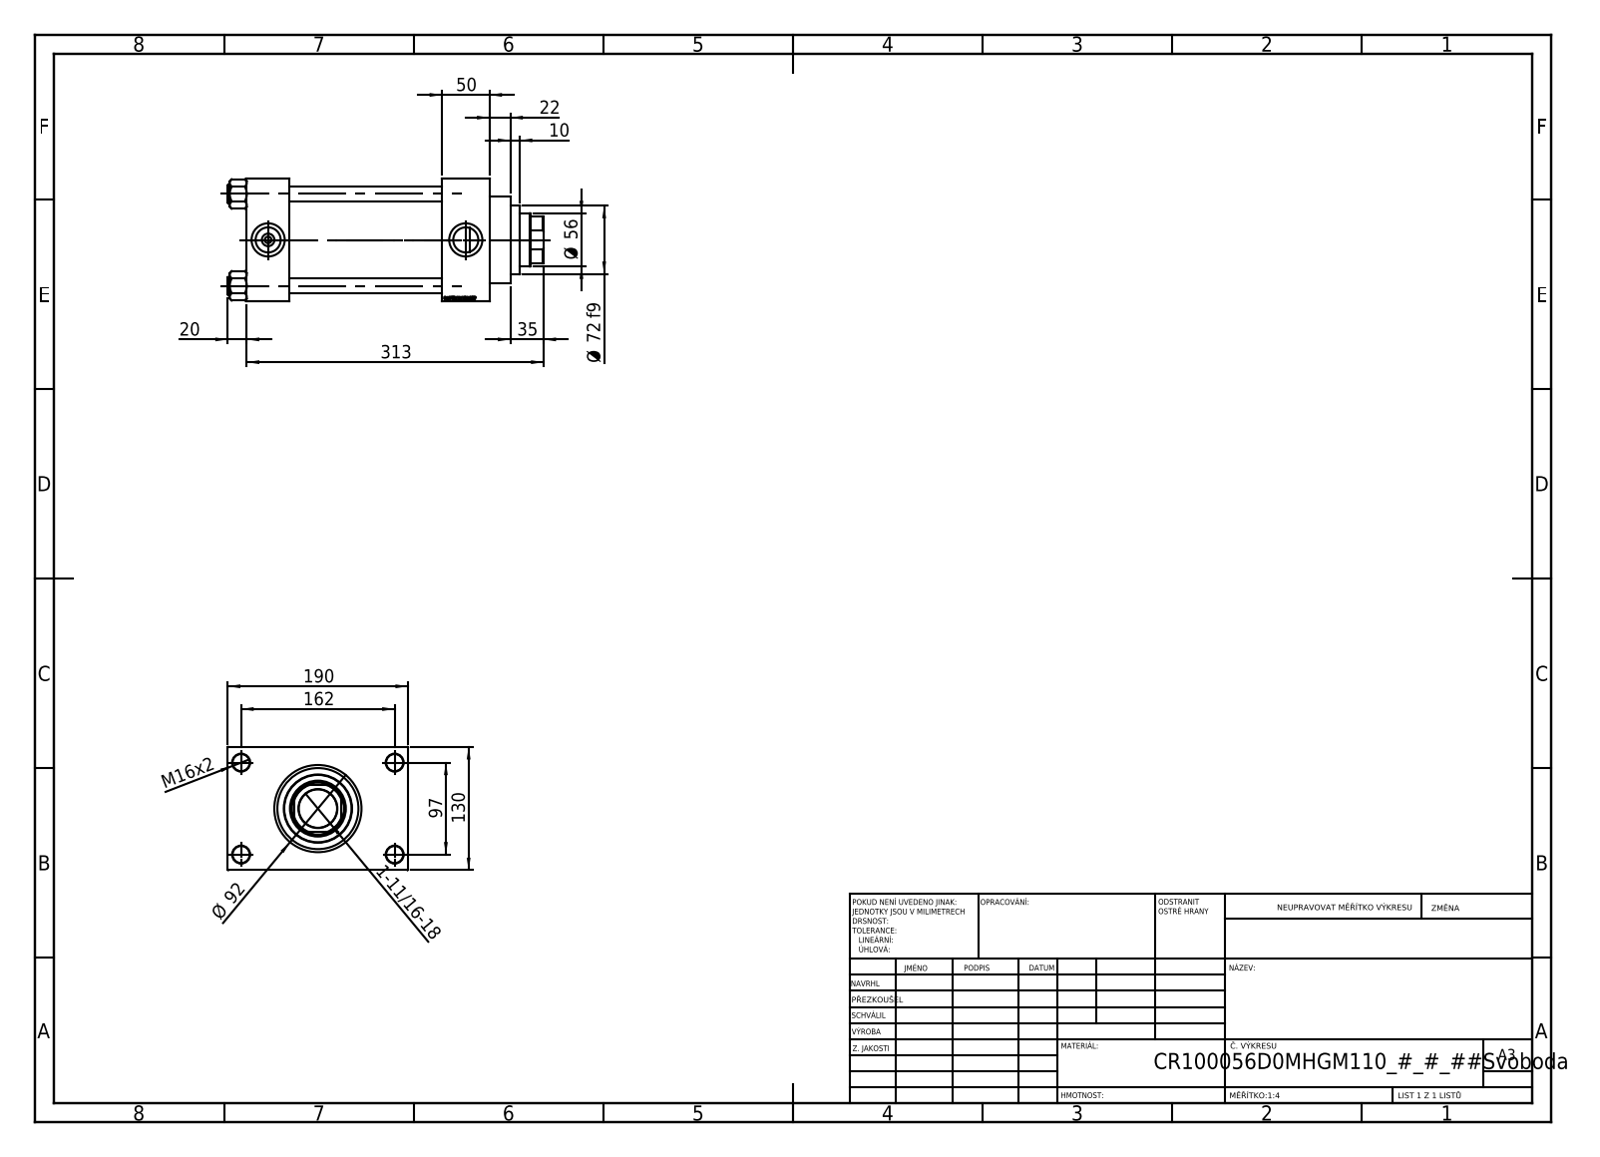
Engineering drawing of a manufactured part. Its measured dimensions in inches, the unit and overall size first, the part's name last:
Units: inches
Overall size (bounding box): 13.11 × 7.48 × 5.118
Round holes (diameter × count): ⌀0.63 ×4, ⌀0.709 ×4, ⌀0.276 ×2, ⌀1.041 ×2, ⌀1.378 ×2, ⌀1.594 ×1, ⌀2.205 ×1, ⌀2.323 ×1, ⌀2.992 ×1, ⌀3.366 ×1, ⌀3.937 ×1
Round bosses / shafts (diameter × count): ⌀0.748 ×4, ⌀4.173 ×1, ⌀3.622 ×1, ⌀2.835 ×1
Partial cylindrical surfaces — rounded edges, fillets, slot ends (radius × count): R1.063 ×1
Main face-to-face distances: 5.118, 1.969, 1.772, 8.11, 6.339, 10.079, 8.307, 6.299, 1.181, 7.48
Hole centre spacings: 1.281, 2.698, 3.717, 3.815, 4.026, 5.096, 6.367, 3.819
Volume: 183.6 in³ · Surface area: 704.5 in²
Bodies: 11 solids, 1151 faces (545 planar, 88 cylindrical, 518 other)
Part name (STEP PRODUCT): V215CR_D_Body; V215_VC_A; NUT_M5_D; V215CR_VCP_D (+1 more)
STEP written by: SolidWorks 2019 (CONFIG_CONTROL_DESIGN)
